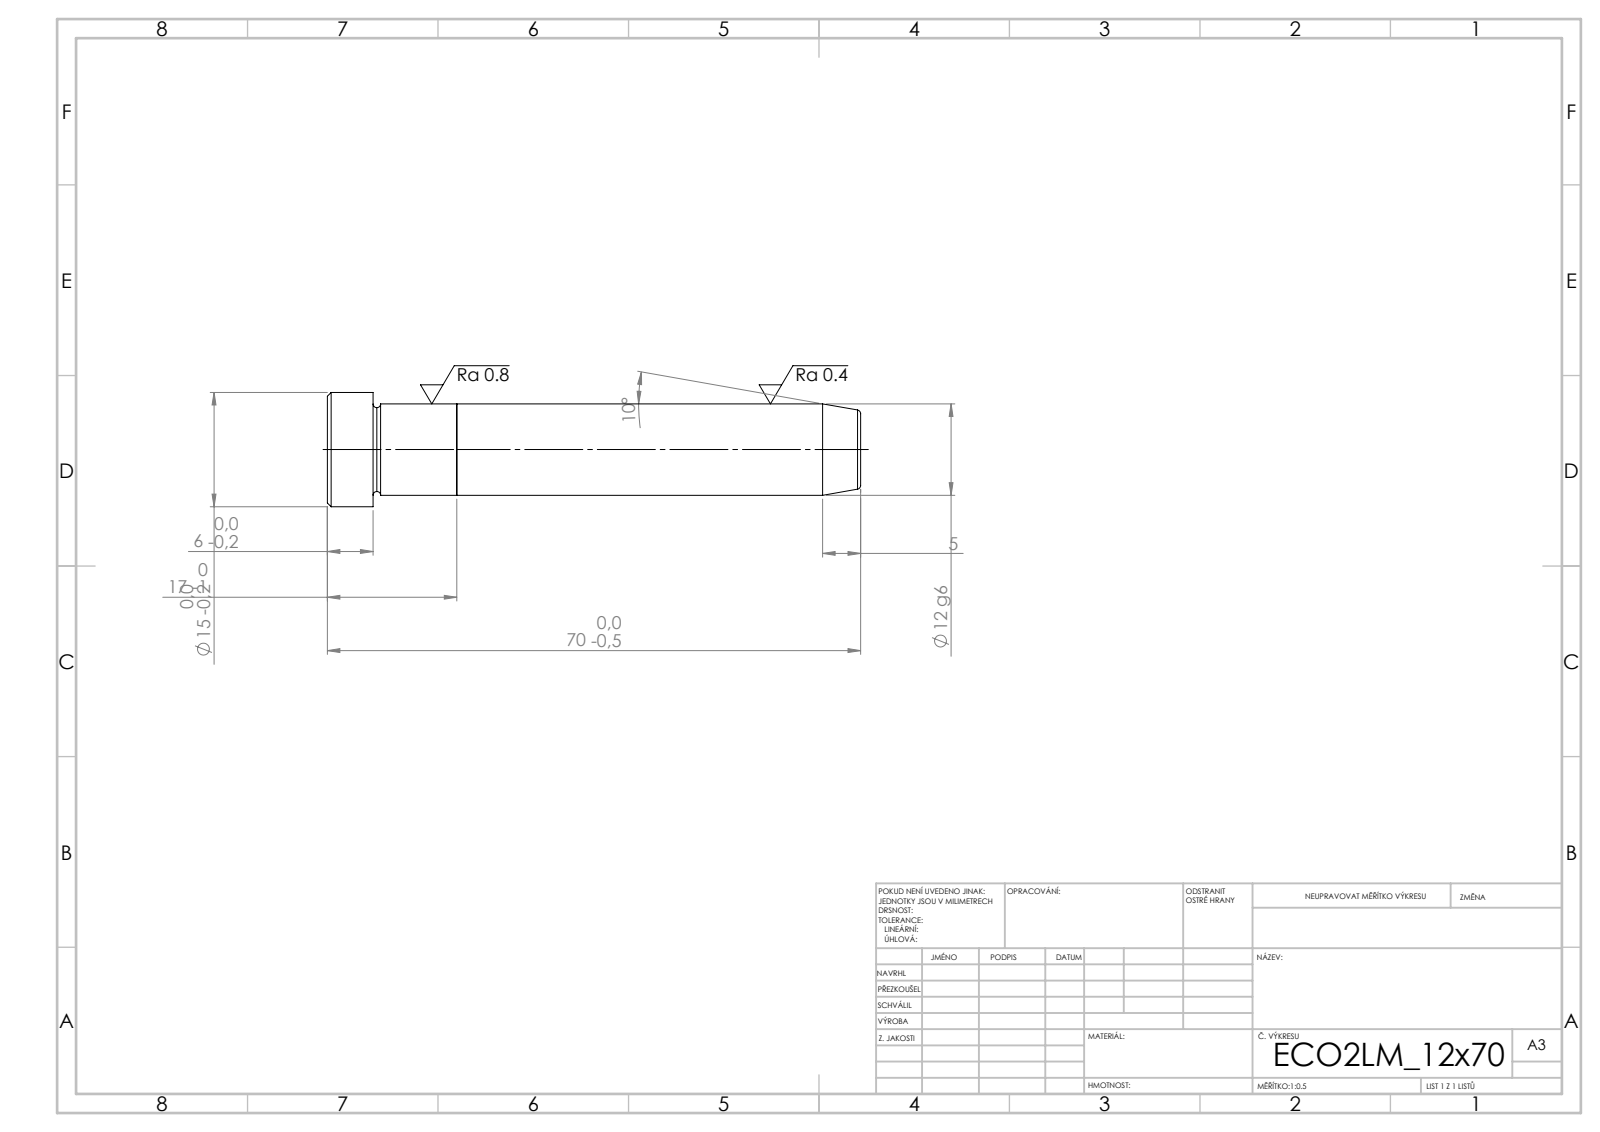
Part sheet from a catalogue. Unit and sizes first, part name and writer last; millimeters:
Units: millimetres
Overall size (bounding box): 70 × 15 × 15
Round bosses / shafts (diameter × count): ⌀15 ×1, ⌀12 ×1
Main face-to-face distances: 17, 53, 70, 64, 11, 6
Volume: 8 198 mm³ · Surface area: 3 233 mm²
Bodies: 2 solids, 21 faces (5 planar, 6 cylindrical, 10 other)
STEP written by: SolidWorks 2019 (CONFIG_CONTROL_DESIGN)
